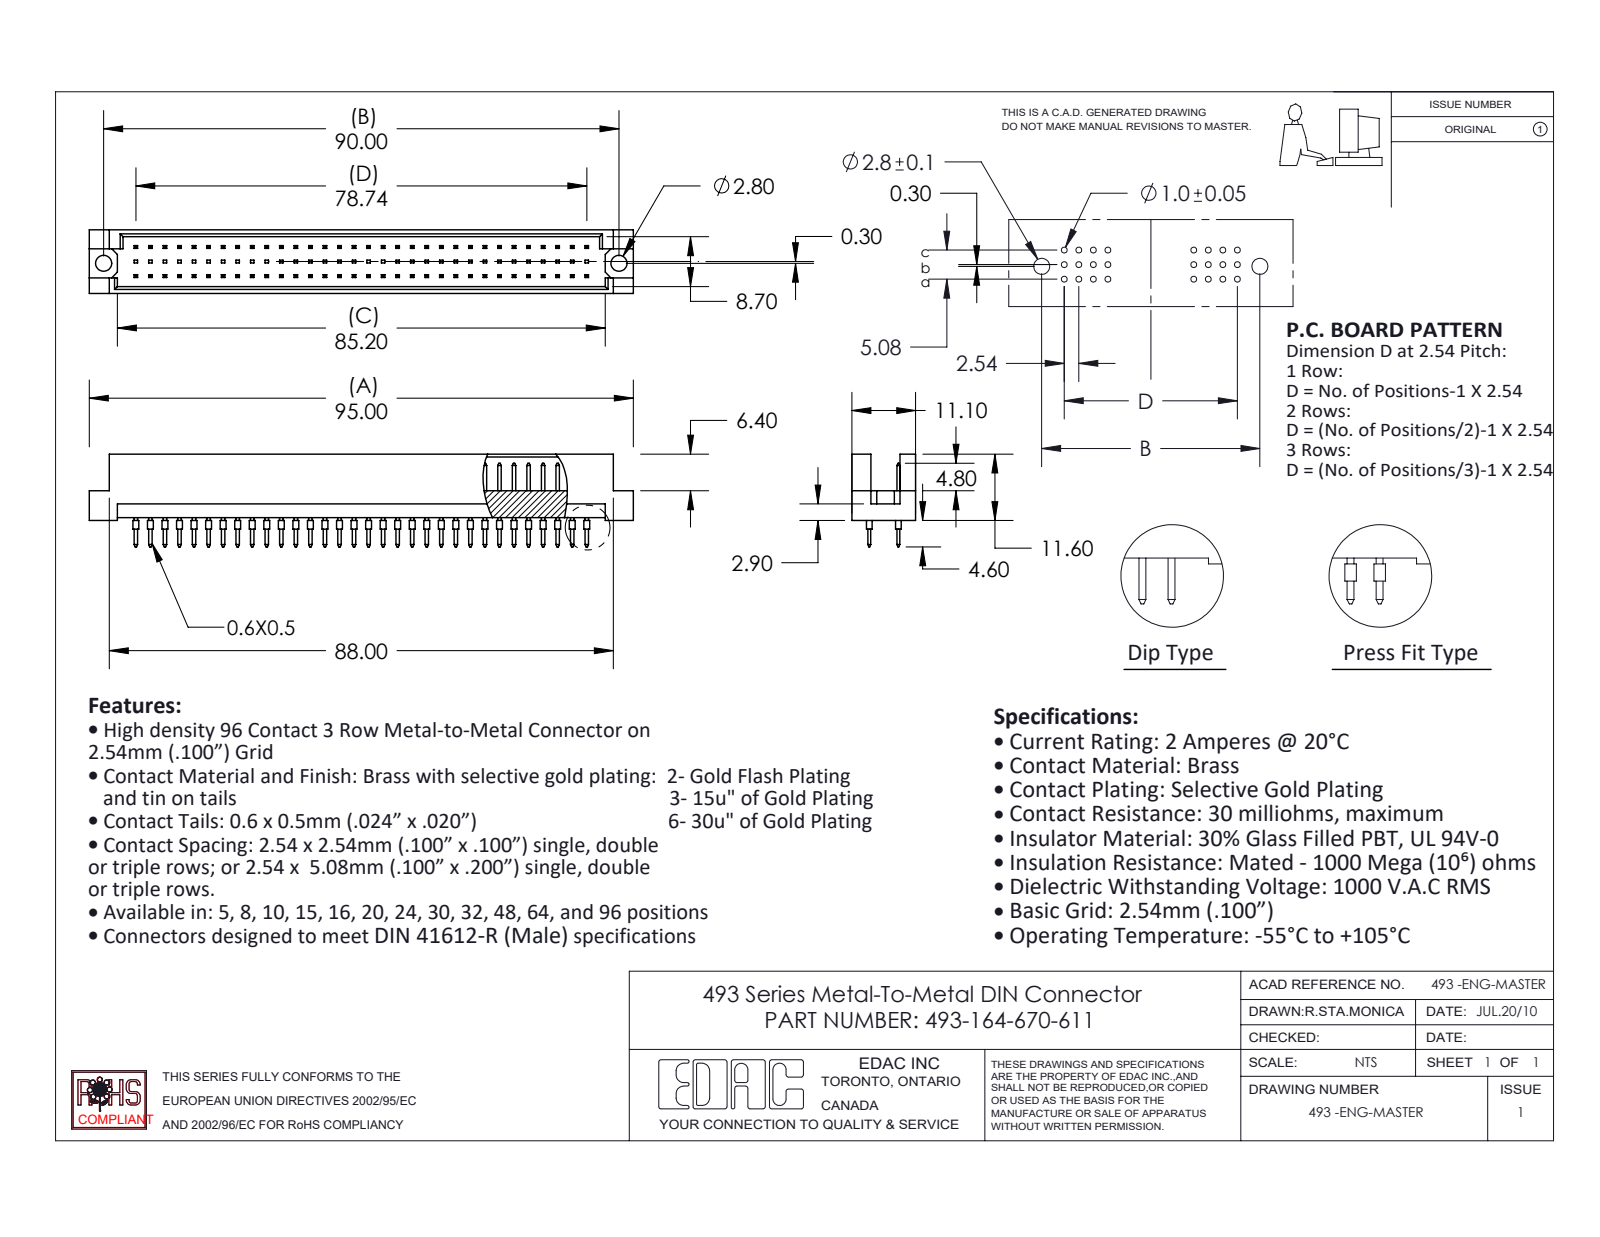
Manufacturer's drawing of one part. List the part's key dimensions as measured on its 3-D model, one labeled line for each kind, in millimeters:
Part name (STEP PRODUCT): 493-164-670-611; 493-290_70; 493 Part_96
STEP written by: SolidWorks 2020 (CONFIG_CONTROL_DESIGN)
Units: millimetres
Bodies: 65 solids, 1844 faces (1712 planar, 132 cylindrical, 0 other)
Overall size (bounding box): 95 × 16.2 × 11.1
Volume: 5 979 mm³ · Surface area: 8 658 mm²
Round holes (diameter × count): ⌀2.8 ×2
Round bosses / shafts (diameter × count): ⌀1 ×64
Main face-to-face distances: 1.2, 9.9, 11.1, 5.08, 0.5, 8.7, 4.7, 2.76, 3.26, 7.84
Hole centre spacings: 90
